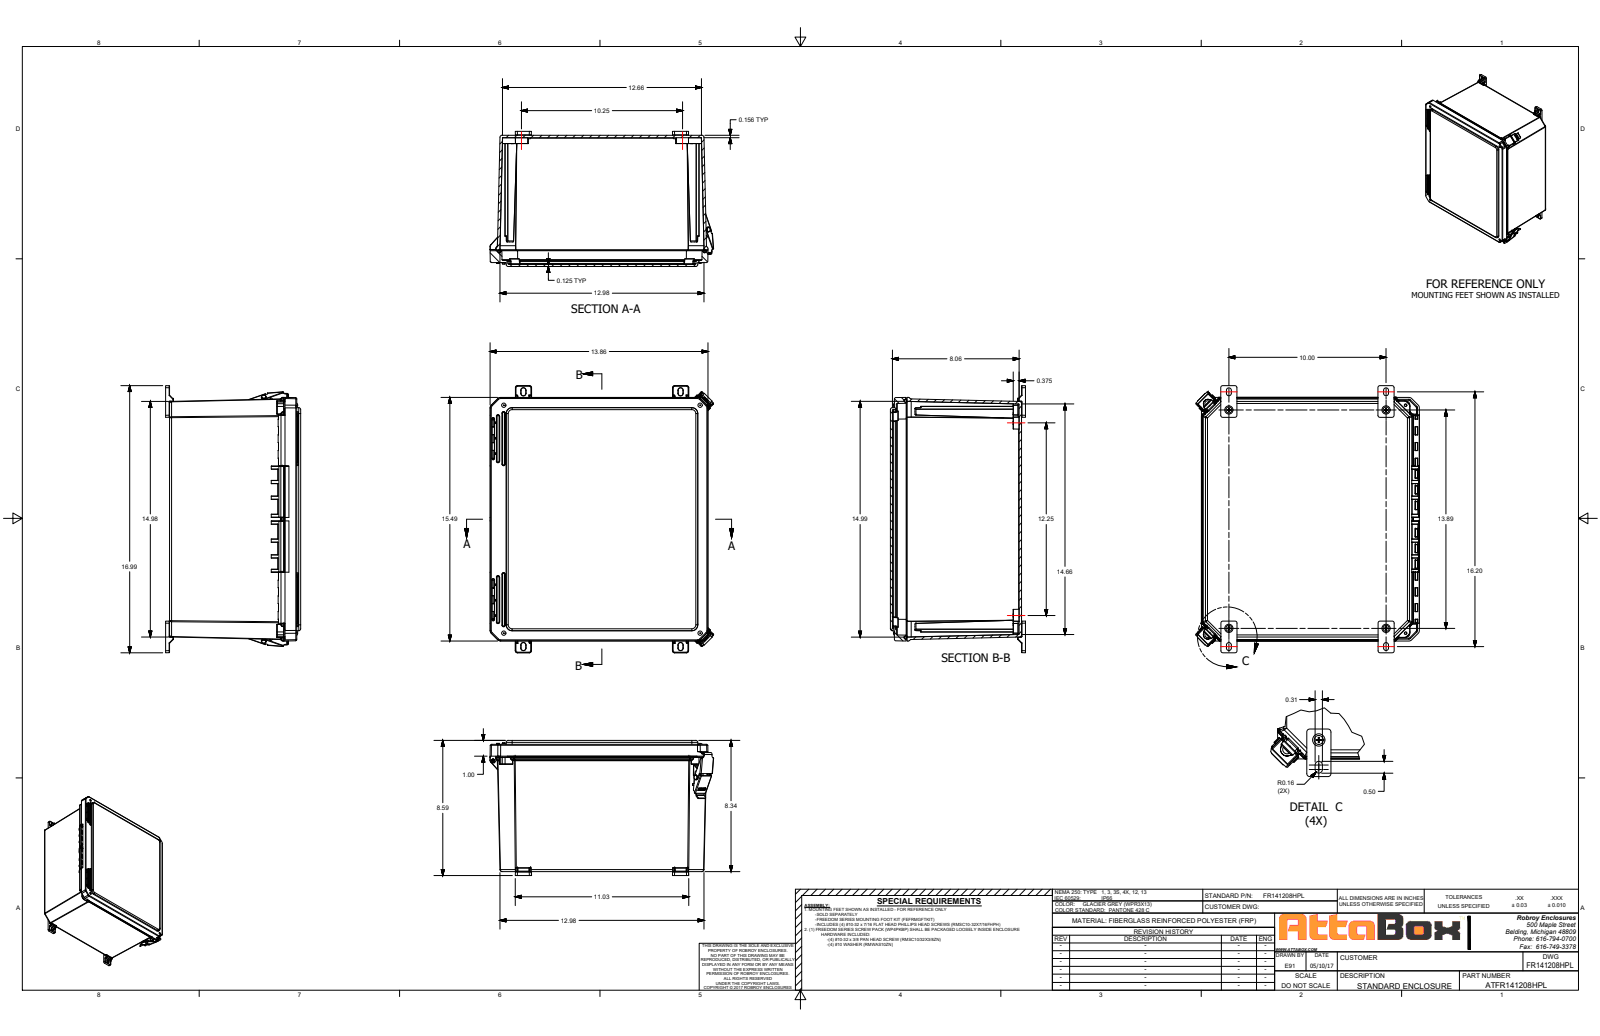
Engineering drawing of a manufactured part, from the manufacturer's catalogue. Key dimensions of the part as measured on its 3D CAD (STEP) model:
Part name (STEP PRODUCT): FR141208HPL
STEP written by: SolidWorks 2021 (AUTOMOTIVE_DESIGN)
Units: inches
Bodies: 29 solids, 2487 faces (812 planar, 1060 cylindrical, 615 other)
Overall size (bounding box): 16.2 × 14.216 × 8.767
Volume: 144.9 in³ · Surface area: 1 846 in²
Round holes (diameter × count): ⌀0.135 ×8, ⌀0.152 ×8, ⌀0.159 ×8, ⌀0.135 ×5, ⌀0.15 ×4, ⌀0.156 ×4, ⌀0.252 ×4, ⌀0.253 ×4, ⌀0.137 ×3, ⌀0.219 ×2, ⌀0.227 ×2, ⌀0.313 ×2
Round bosses / shafts (diameter × count): ⌀0.27 ×8, ⌀0.3 ×4, ⌀0.262 ×4, ⌀0.209 ×4, ⌀0.135 ×3, ⌀0.435 ×2, ⌀0.135 ×1
Partial cylindrical surfaces — rounded edges, fillets, slot ends (radius × count): R0.01 ×186, R0.005 ×110, R0.03 ×70, R0.02 ×54, R0.06 ×36, R0.09 ×26, R0.03 ×24, R0.096 ×24
Main face-to-face distances: 0.156, 0.16, 8.183, 8.339, 0.125, 8.058, 8.213, 0.158, 0.159, 0.25
Hole centre spacings: 14.243, 13.417, 0.25, 13.836, 14.489, 17.55, 13.069, 14.49
